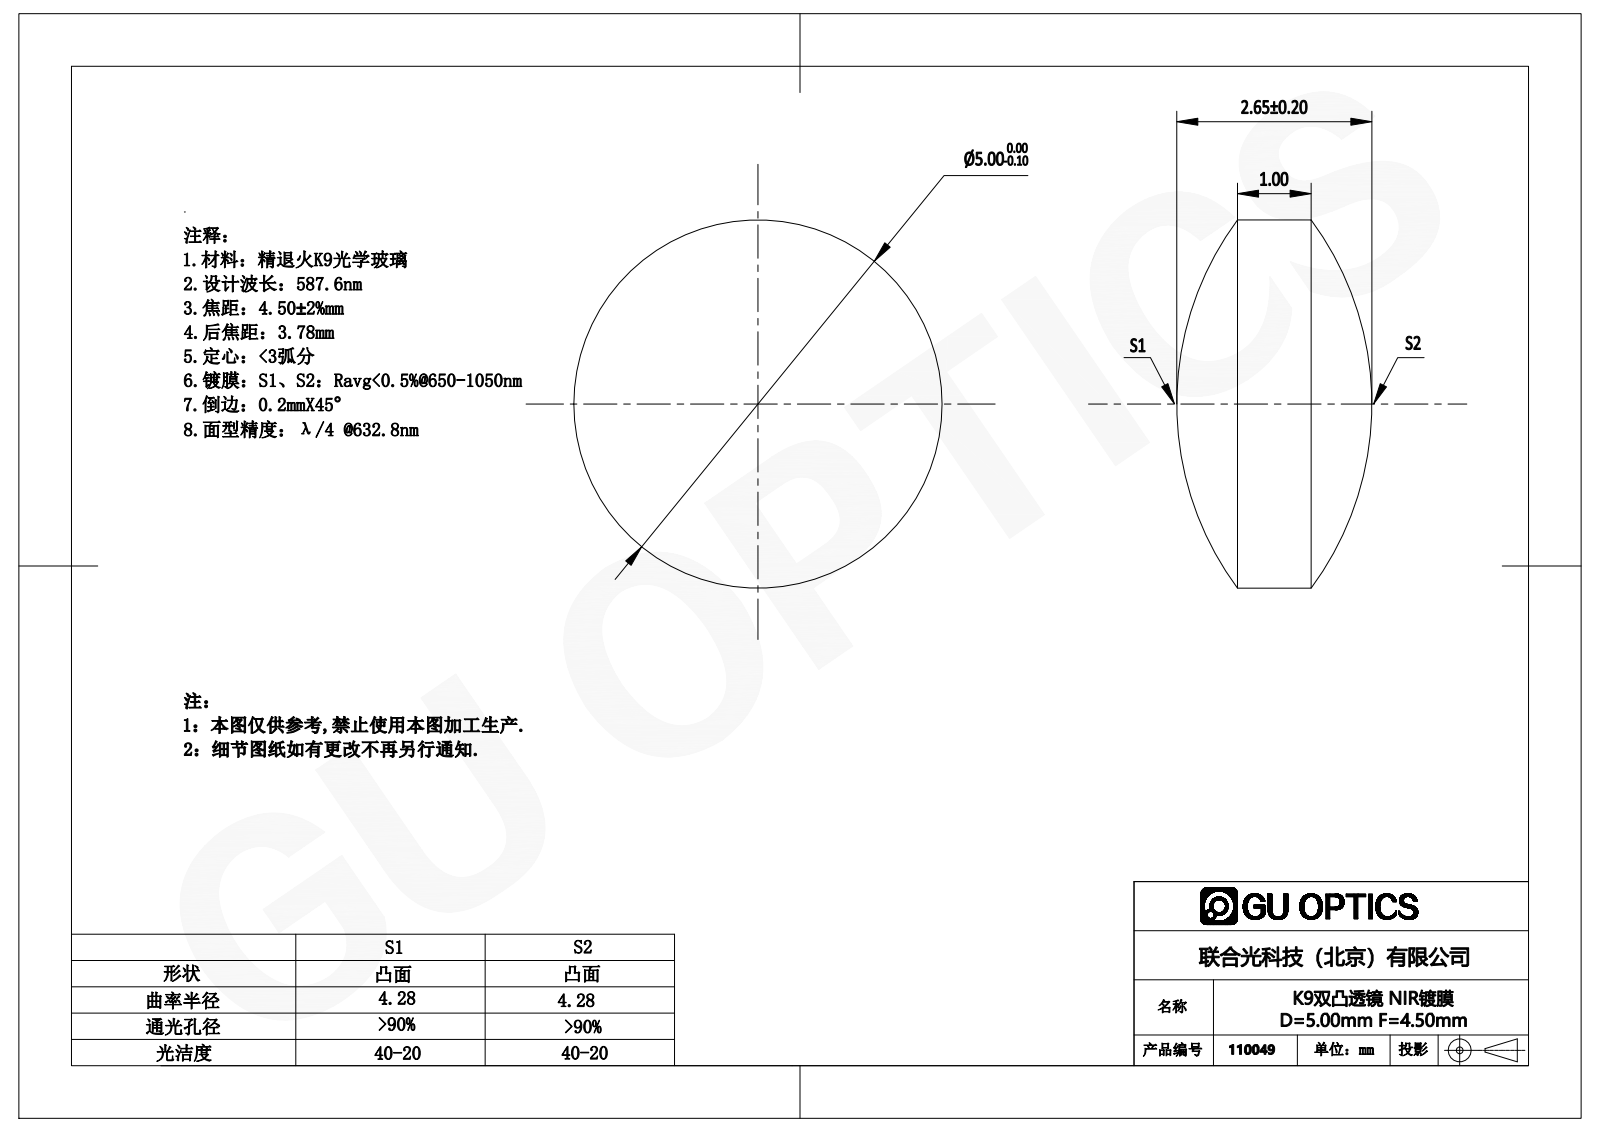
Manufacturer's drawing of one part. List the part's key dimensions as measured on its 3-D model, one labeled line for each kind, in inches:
Part name (STEP PRODUCT): 110005
STEP written by: SolidWorks 2016 (CONFIG_CONTROL_DESIGN)
Units: inches
Bodies: 1 solid, 6 faces (0 planar, 2 cylindrical, 4 other)
Overall size (bounding box): 0.197 × 0.197 × 0.104
Volume: 0.002 in³ · Surface area: 0.091 in²
Round bosses / shafts (diameter × count): ⌀0.197 ×1
